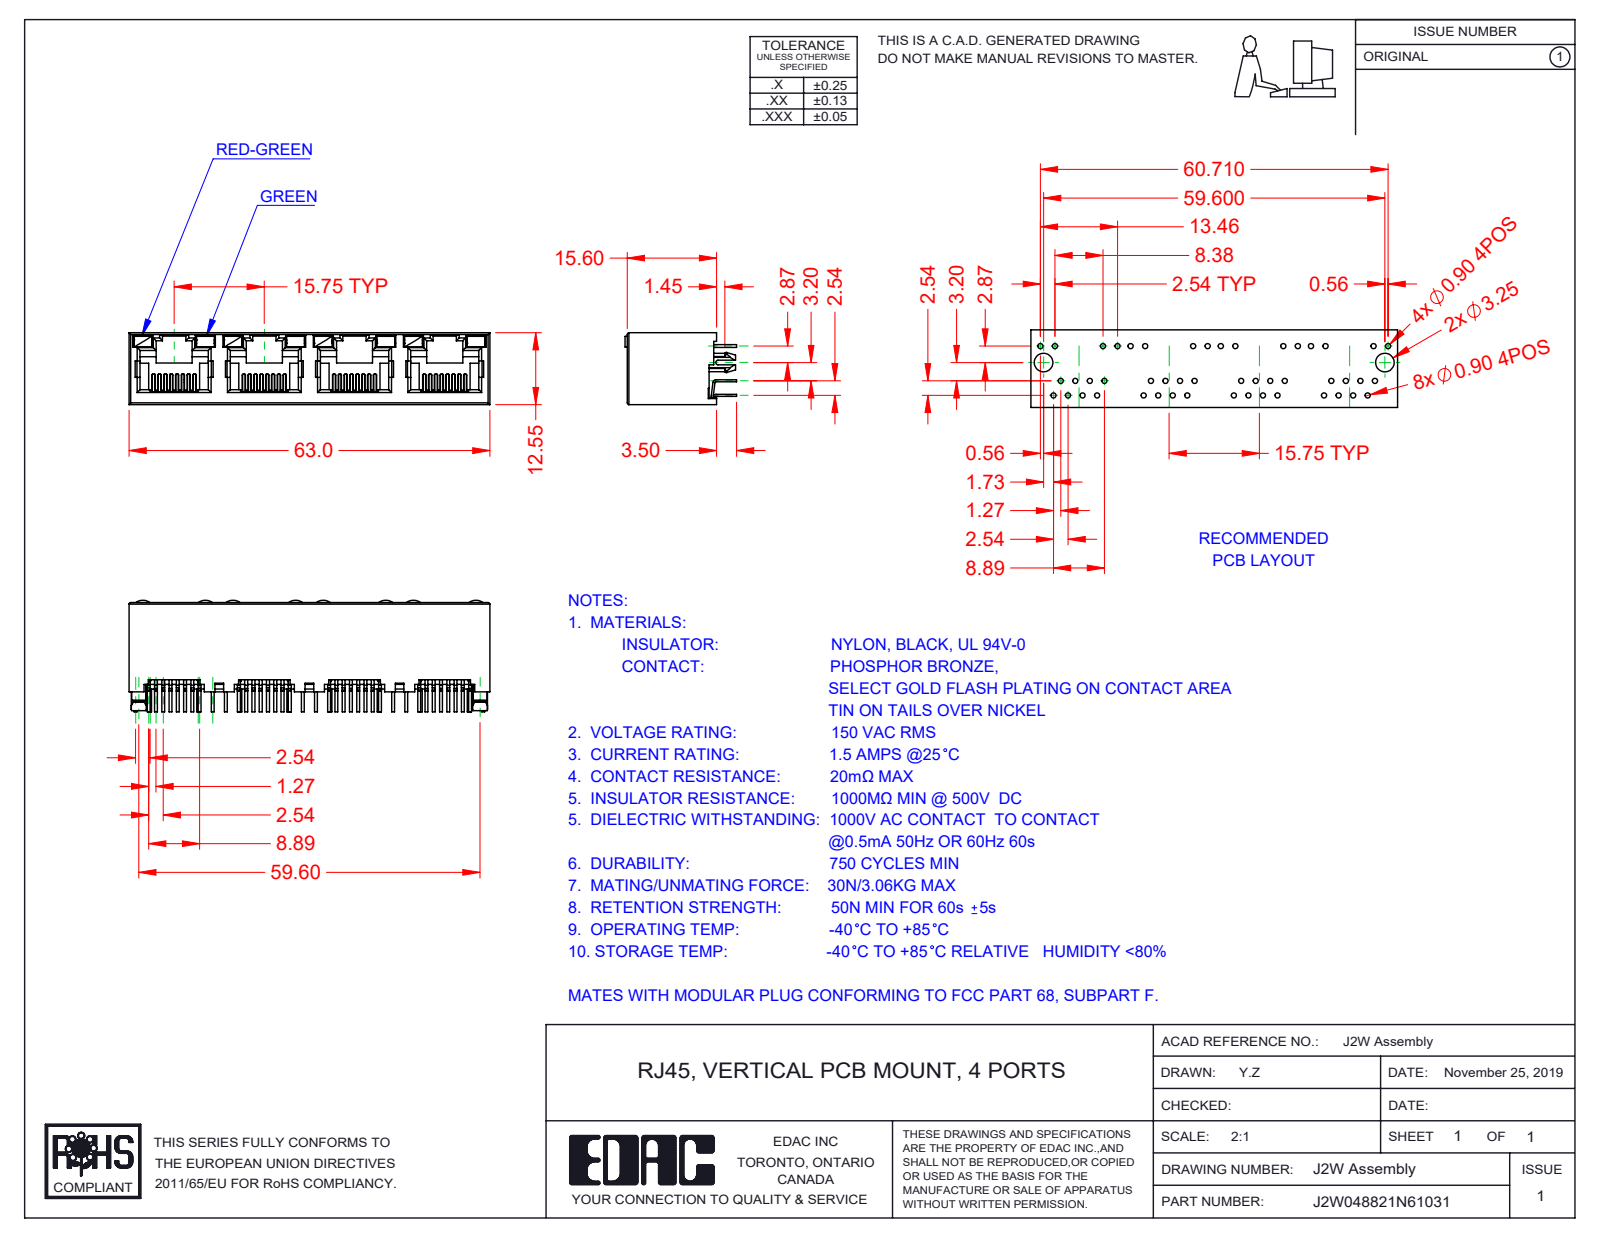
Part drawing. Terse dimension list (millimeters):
name: 2W LED LH_6-Red-Green; 2W Contacts; 2W Contact Lock; 2W Insulator (+2 more)
written by: SolidWorks 2016 (CONFIG_CONTROL_DESIGN)
unit: mm
bodies: 45 solids, 3139 faces (2600 planar, 481 cylindrical, 58 other)
size: 63 × 19.5 × 12.55
volume: 5 335 mm³; area: 13 144 mm²
rounds: 64× R0.15, 29× R0.2, 28× R0.5, 14× R0.3, 8× R0.45, 8× R2, 2× R0.25, 2× R1.5
face distances: 12.55, 11.9, 0.65, 15.75, 0.36, 1.5, 0.78, 0.6, 11.3, 31.5
